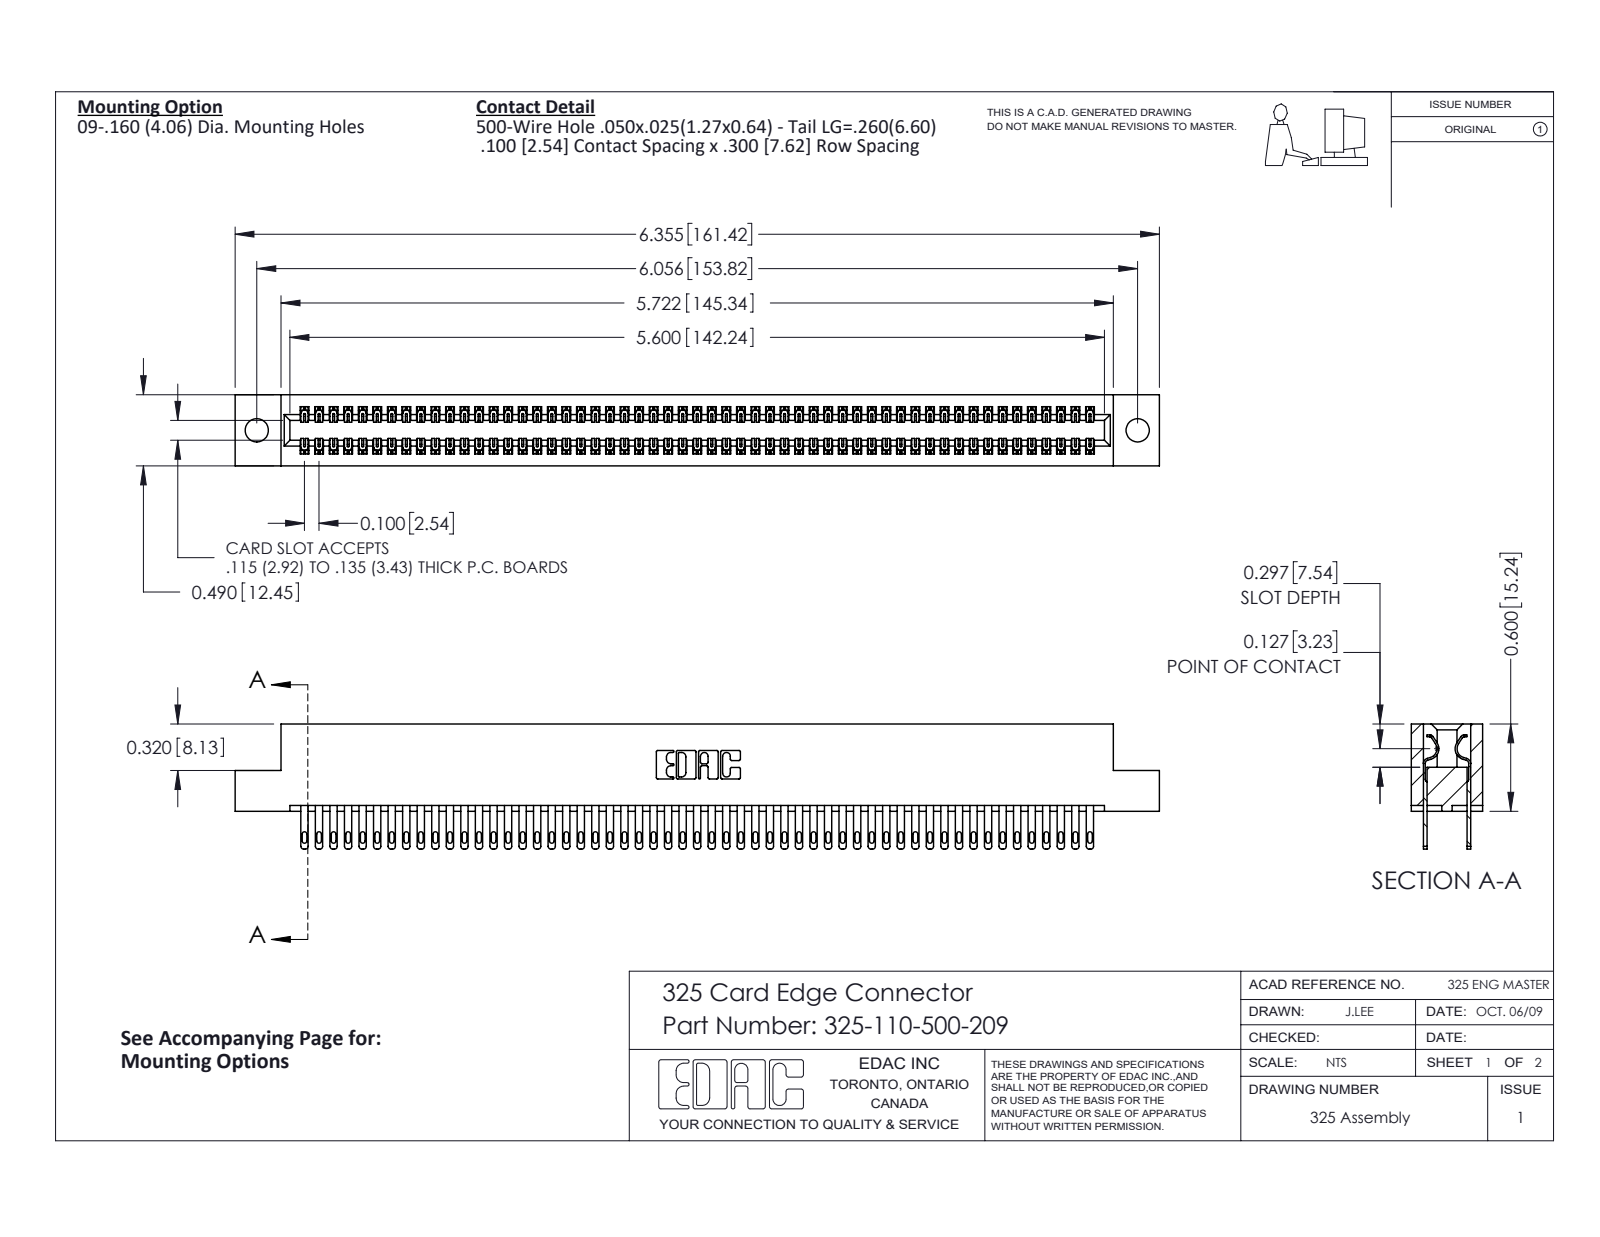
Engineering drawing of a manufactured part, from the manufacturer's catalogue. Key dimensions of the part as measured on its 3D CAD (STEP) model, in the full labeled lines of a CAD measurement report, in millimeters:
Part name (STEP PRODUCT): 325-110-500-209; 325 Part_.160 TH; 325-292-001_325-293-100
STEP written by: SolidWorks 2016 (CONFIG_CONTROL_DESIGN)
Units: millimetres
Bodies: 111 solids, 5394 faces (3370 planar, 2024 cylindrical, 0 other)
Overall size (bounding box): 161.4 × 21.8 × 12.4
Volume: 21 060 mm³ · Surface area: 26 870 mm²
Round holes (diameter × count): ⌀4.1 ×2
Partial cylindrical surfaces — rounded edges, fillets, slot ends (radius × count): R0.2 ×165, R0.4 ×110, R0.5 ×110, R0.3 ×22, R0.2 ×6, R0.8 ×6, R0.7 ×3, R0.4 ×2
Main face-to-face distances: 2.1, 10.3, 7.6, 2.7, 9.7, 0.6, 12.4, 8.3, 7, 6.7
Hole centre spacings: 153.8
